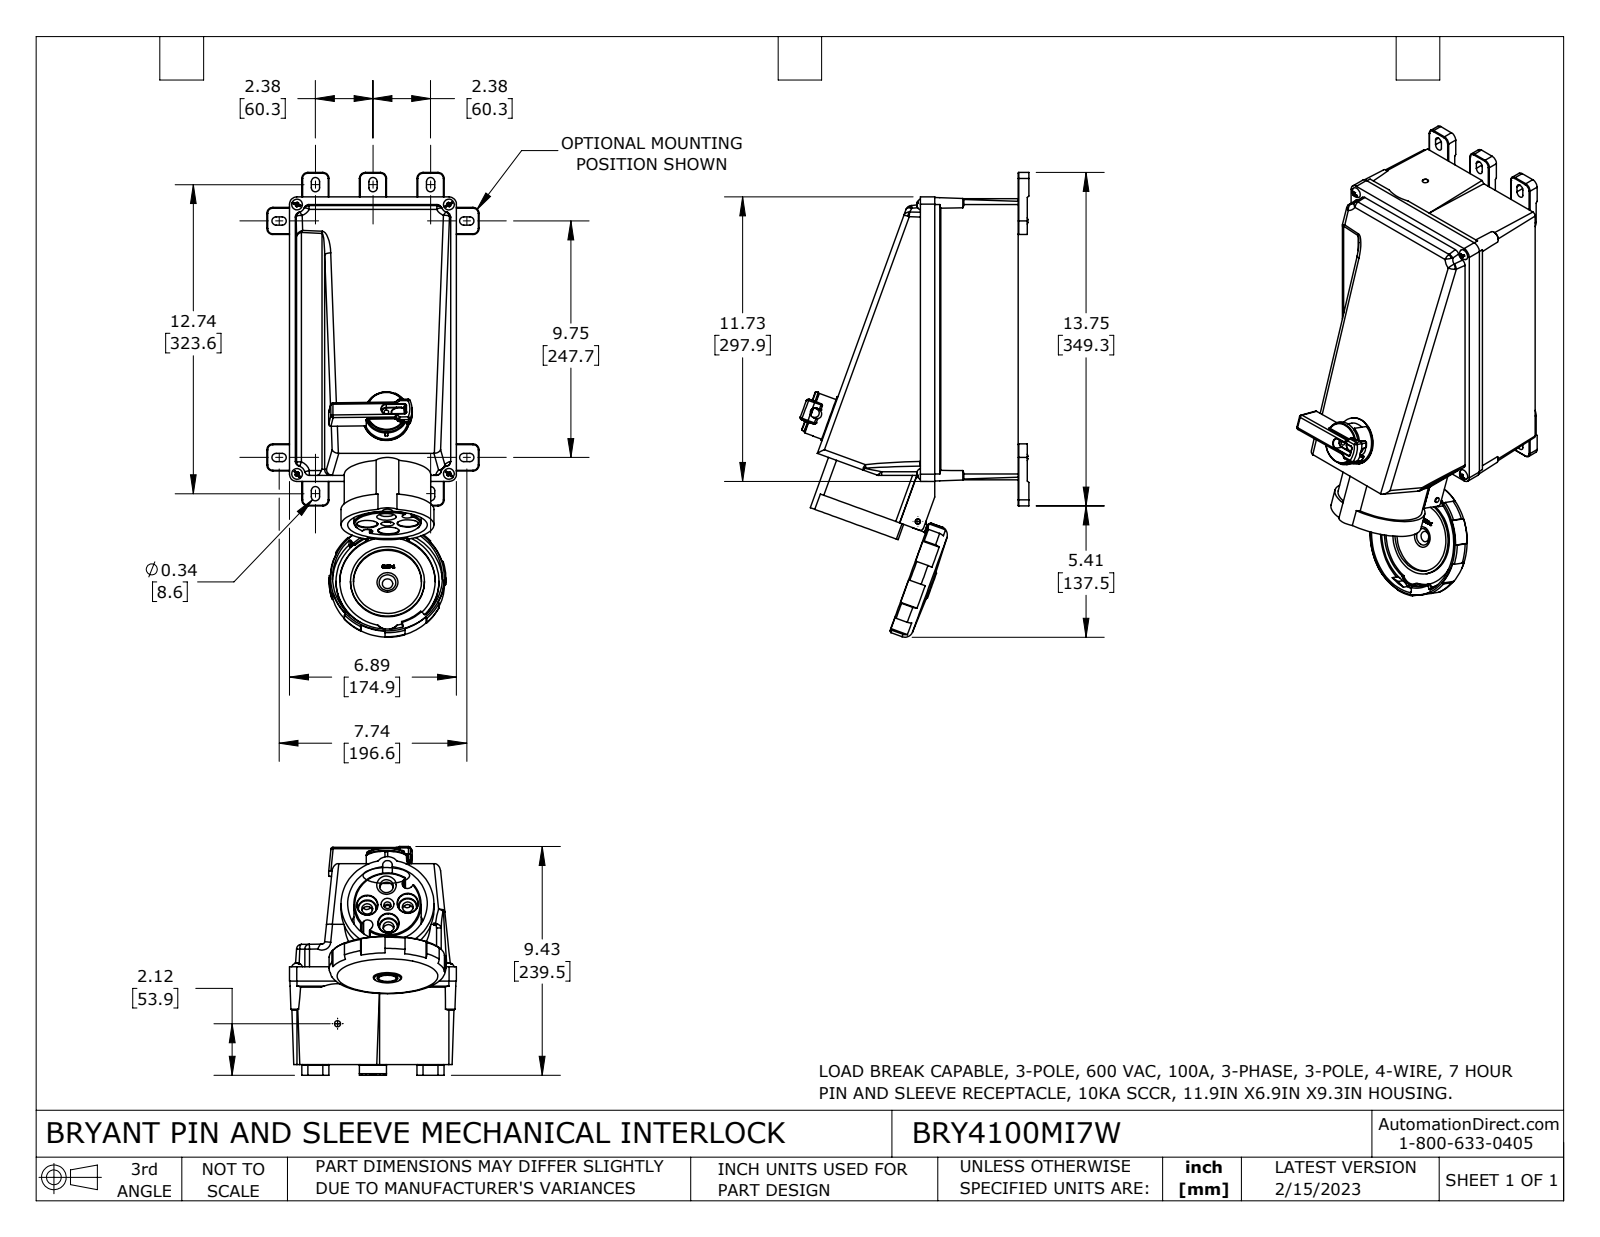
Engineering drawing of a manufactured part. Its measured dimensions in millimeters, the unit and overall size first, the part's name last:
Units: millimetres
Overall size (bounding box): 486.8 × 239.5 × 174.9
Round holes (diameter × count): ⌀7.1 ×5, ⌀7.1 ×3, ⌀2.5 ×2, ⌀3.1 ×2, ⌀5.8 ×2, ⌀6.4 ×2, ⌀4.2 ×1, ⌀4.2 ×1, ⌀4.8 ×1, ⌀5.3 ×1, ⌀19.7 ×1, ⌀21.8 ×1
Round bosses / shafts (diameter × count): ⌀6.7 ×2, ⌀107.8 ×1, ⌀77.4 ×1, ⌀72 ×1, ⌀70.5 ×1, ⌀48.8 ×1, ⌀31.6 ×1, ⌀20.3 ×1
Partial cylindrical surfaces — rounded edges, fillets, slot ends (radius × count): R0.4 ×115, R0.8 ×30, R2 ×30, R2.3 ×19, R6.4 ×19, R0.5 ×16, R1.9 ×12, R4.3 ×10
Main face-to-face distances: 87.4, 154.3, 0.9, 153.4, 294.5, 102.4, 15, 3, 3.8, 174.9
Hole centre spacings: 17.5, 17.5, 62, 62, 127.7, 127.7, 30.4, 31
Volume: 7 844 000 mm³ · Surface area: 580 500 mm²
Bodies: 15 solids, 2241 faces (806 planar, 700 cylindrical, 735 other)
Part name (STEP PRODUCT): BRY4100MI7W
STEP written by: SolidWorks 2021 (CONFIG_CONTROL_DESIGN)
